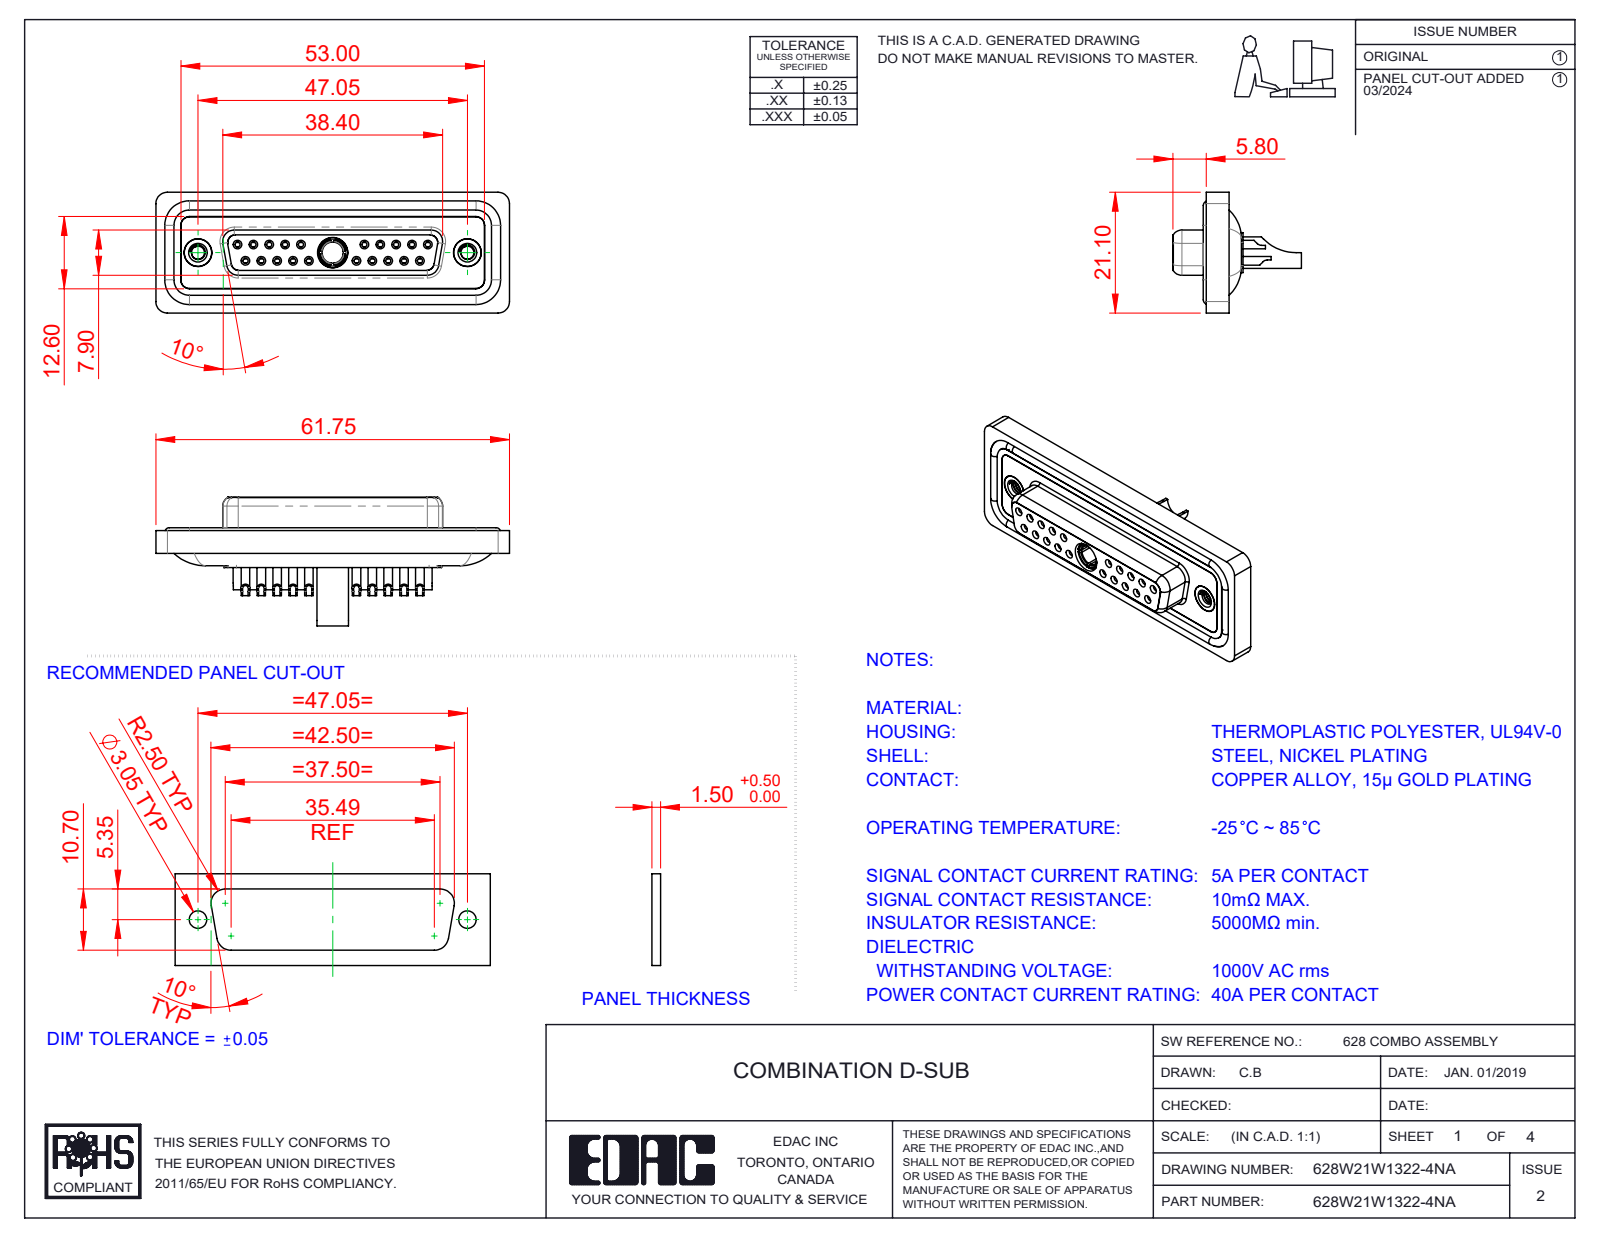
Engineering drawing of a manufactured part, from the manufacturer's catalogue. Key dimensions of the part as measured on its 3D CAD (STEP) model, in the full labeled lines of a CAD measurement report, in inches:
Part name (STEP PRODUCT): 628Combo Contact Row 2_22; 628Combo Housing_21W1; 628Combo Shell Front_25 Contacts; 628Combo Waterproof Housing_25 Contacts (+5 more)
STEP written by: SolidWorks 2023 (CONFIG_CONTROL_DESIGN)
Units: inches
Bodies: 29 solids, 1561 faces (476 planar, 634 cylindrical, 451 other)
Overall size (bounding box): 2.431 × 0.884 × 0.831
Volume: 0.516 in³ · Surface area: 22.24 in²
Round holes (diameter × count): ⌀0.035 ×20, ⌀0.039 ×20, ⌀0.043 ×20, ⌀0.059 ×20, ⌀0.079 ×20, ⌀0.063 ×10, ⌀0.067 ×10, ⌀0.191 ×3, ⌀0.089 ×2, ⌀0.157 ×2, ⌀0.159 ×2, ⌀0.197 ×2
Round bosses / shafts (diameter × count): ⌀0.087 ×20, ⌀0.063 ×14, ⌀0.195 ×2, ⌀0.189 ×2, ⌀0.217 ×1, ⌀0.205 ×1, ⌀0.195 ×1, ⌀0.187 ×1
Partial cylindrical surfaces — rounded edges, fillets, slot ends (radius × count): R0.059 ×22, R0.079 ×18, R0.053 ×8, R0.063 ×8, R0.039 ×6, R0.01 ×4, R0.02 ×4, R0.024 ×4
Main face-to-face distances: 0.016, 0.071, 0.293, 0.222, 0.26, 0.02, 0.063, 0.278, 0.114, 0.043
Hole centre spacings: 0.124, 0.109, 0.218, 0.198, 0.327, 0.294, 0.654, 0.763
